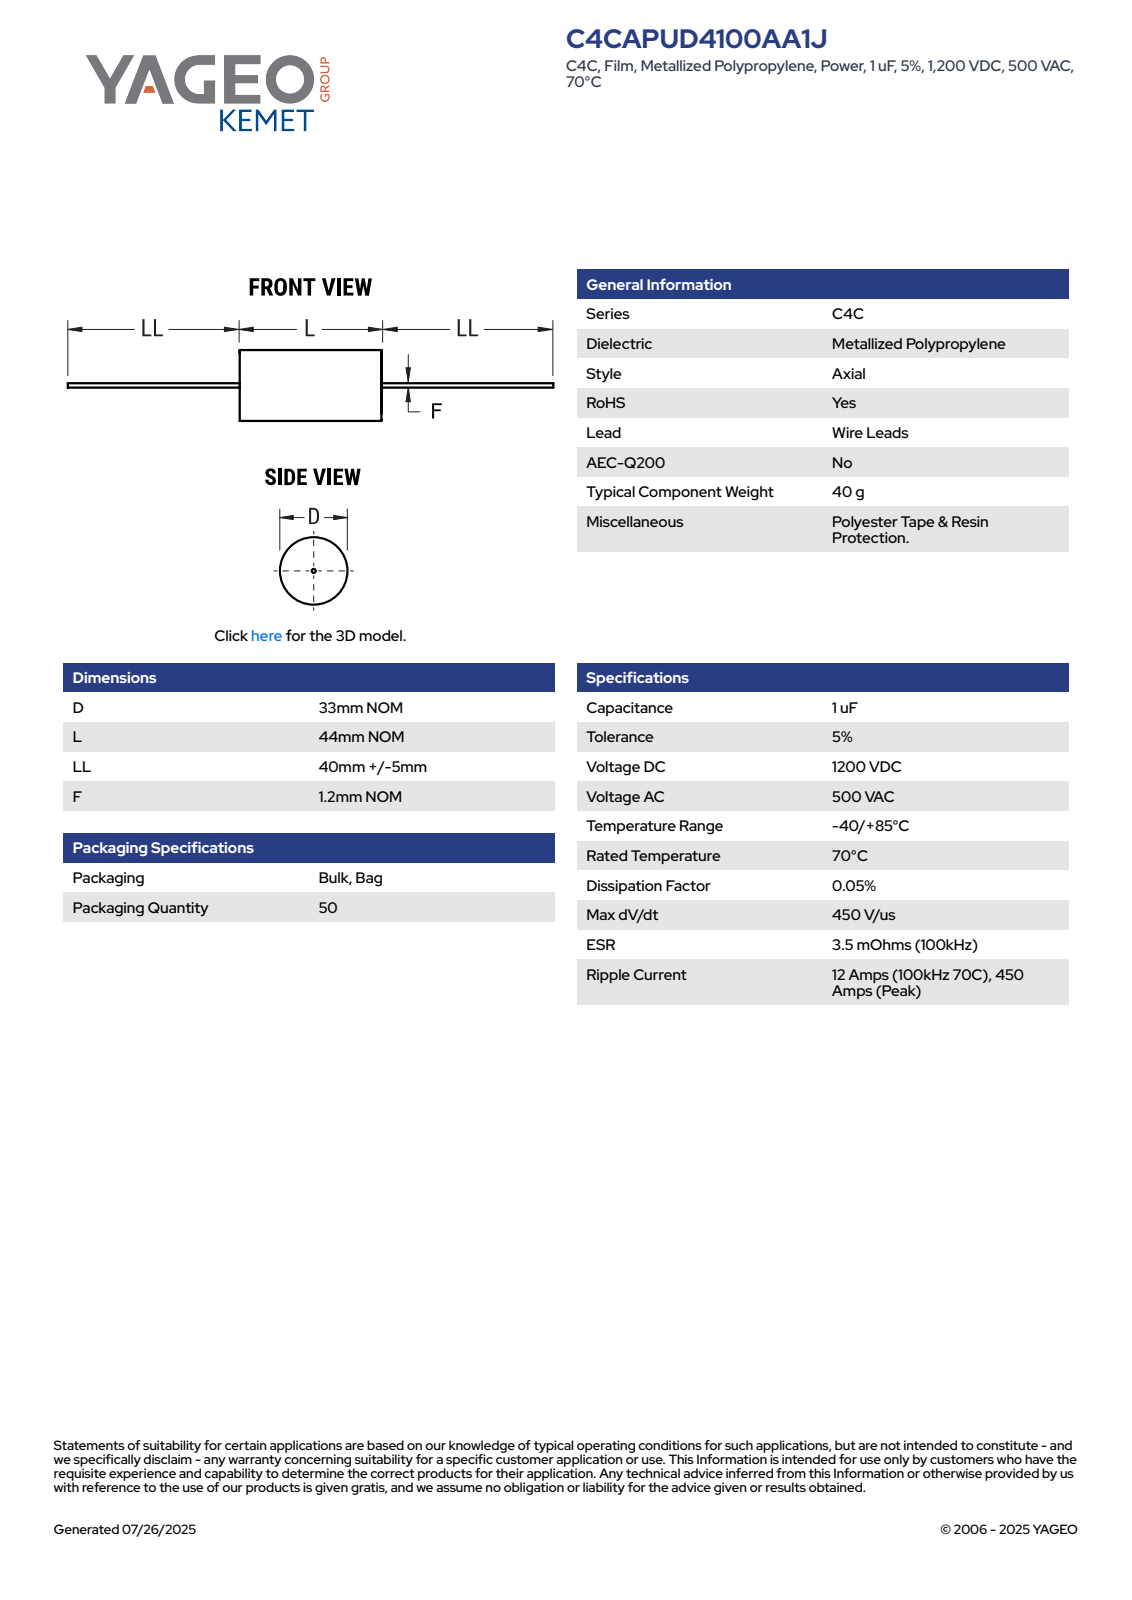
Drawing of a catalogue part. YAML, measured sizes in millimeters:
part_name: "CFP_ACWF_33X44_D33L44LL45F1.2"
step_written_by: "SolidWorks 2014 (AUTOMOTIVE_DESIGN)"
units: millimeters
bodies: {solids: 2, faces: 87, planar: 28, cylindrical: 28, other: 31}
overall_size: [134, 33, 33]
volume: 37735
surface_area: 8321
round_bosses_or_shafts:
  - {diameter: 33, count: 1}
  - {diameter: 1.2, count: 1}
partial_cylinders:
  - {radius: 16.49, count: 1}
face_to_face_distances: [44, 43.99, 44.99, 45, 88.99, 134, 89.01, 89, 45.01]
